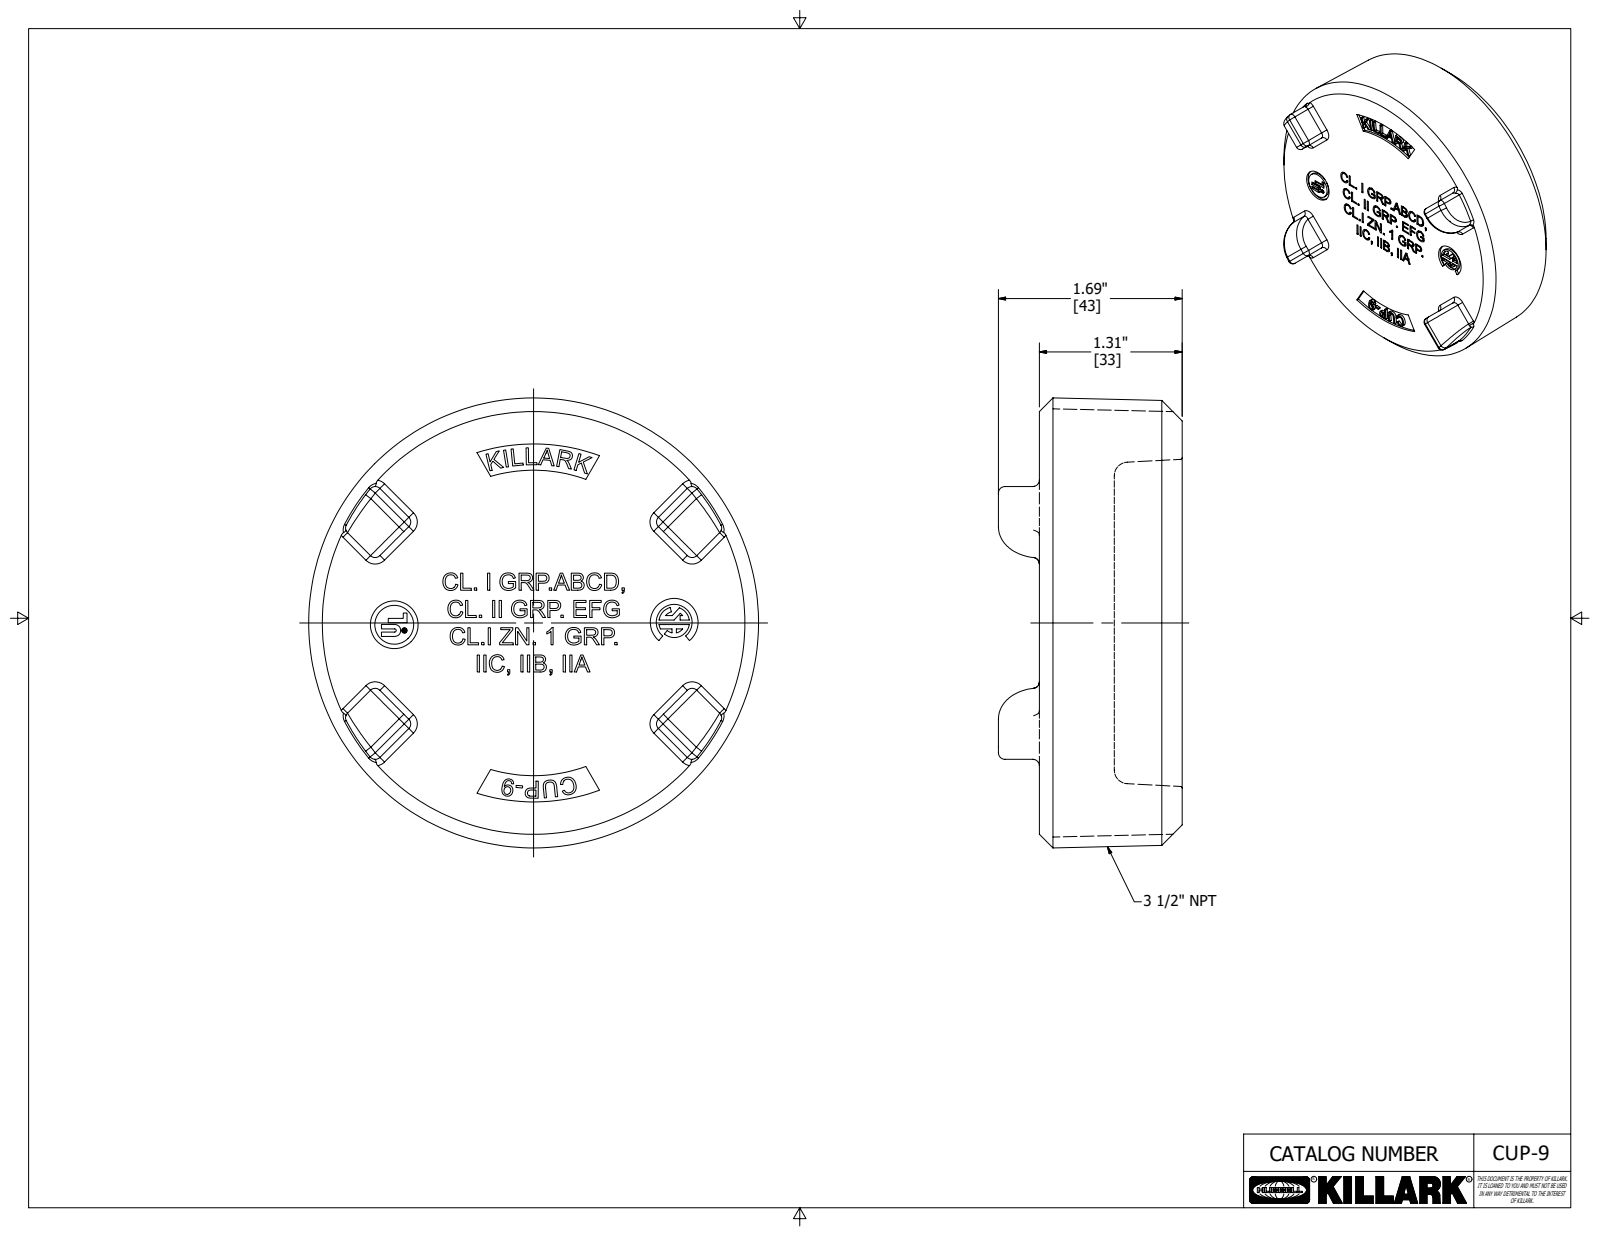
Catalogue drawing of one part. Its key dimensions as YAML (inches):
part_name: "CUP-9_ETO"
step_written_by: "Autodesk Inventor 2020 (AUTOMOTIVE_DESIGN)"
units: inches
bodies: {solids: 1, faces: 757, planar: 500, cylindrical: 56, other: 201}
overall_size: [4.125, 4.125, 1.685]
volume: 12.96
surface_area: 49.75
round_holes:
  - {diameter: 0.048, count: 1}
  - {diameter: 0.437, count: 1}
round_bosses_or_shafts:
  - {diameter: 0.356, count: 1}
  - {diameter: 0.043, count: 1}
partial_cylinders:
  - {radius: 0.06, count: 28}
  - {radius: 0.375, count: 4}
  - {radius: 1.75, count: 2}
  - {radius: 0.014, count: 1}
  - {radius: 0.055, count: 1}
  - {radius: 0.099, count: 1}
  - {radius: 0.14, count: 1}
  - {radius: 0.164, count: 1}
face_to_face_distances: [0.687, 0.622, 1.31, 0.656, 0.031, 1.279, 1.308, 1.558, 0.25, 0.654]
hole_center_spacings: [0.107]
